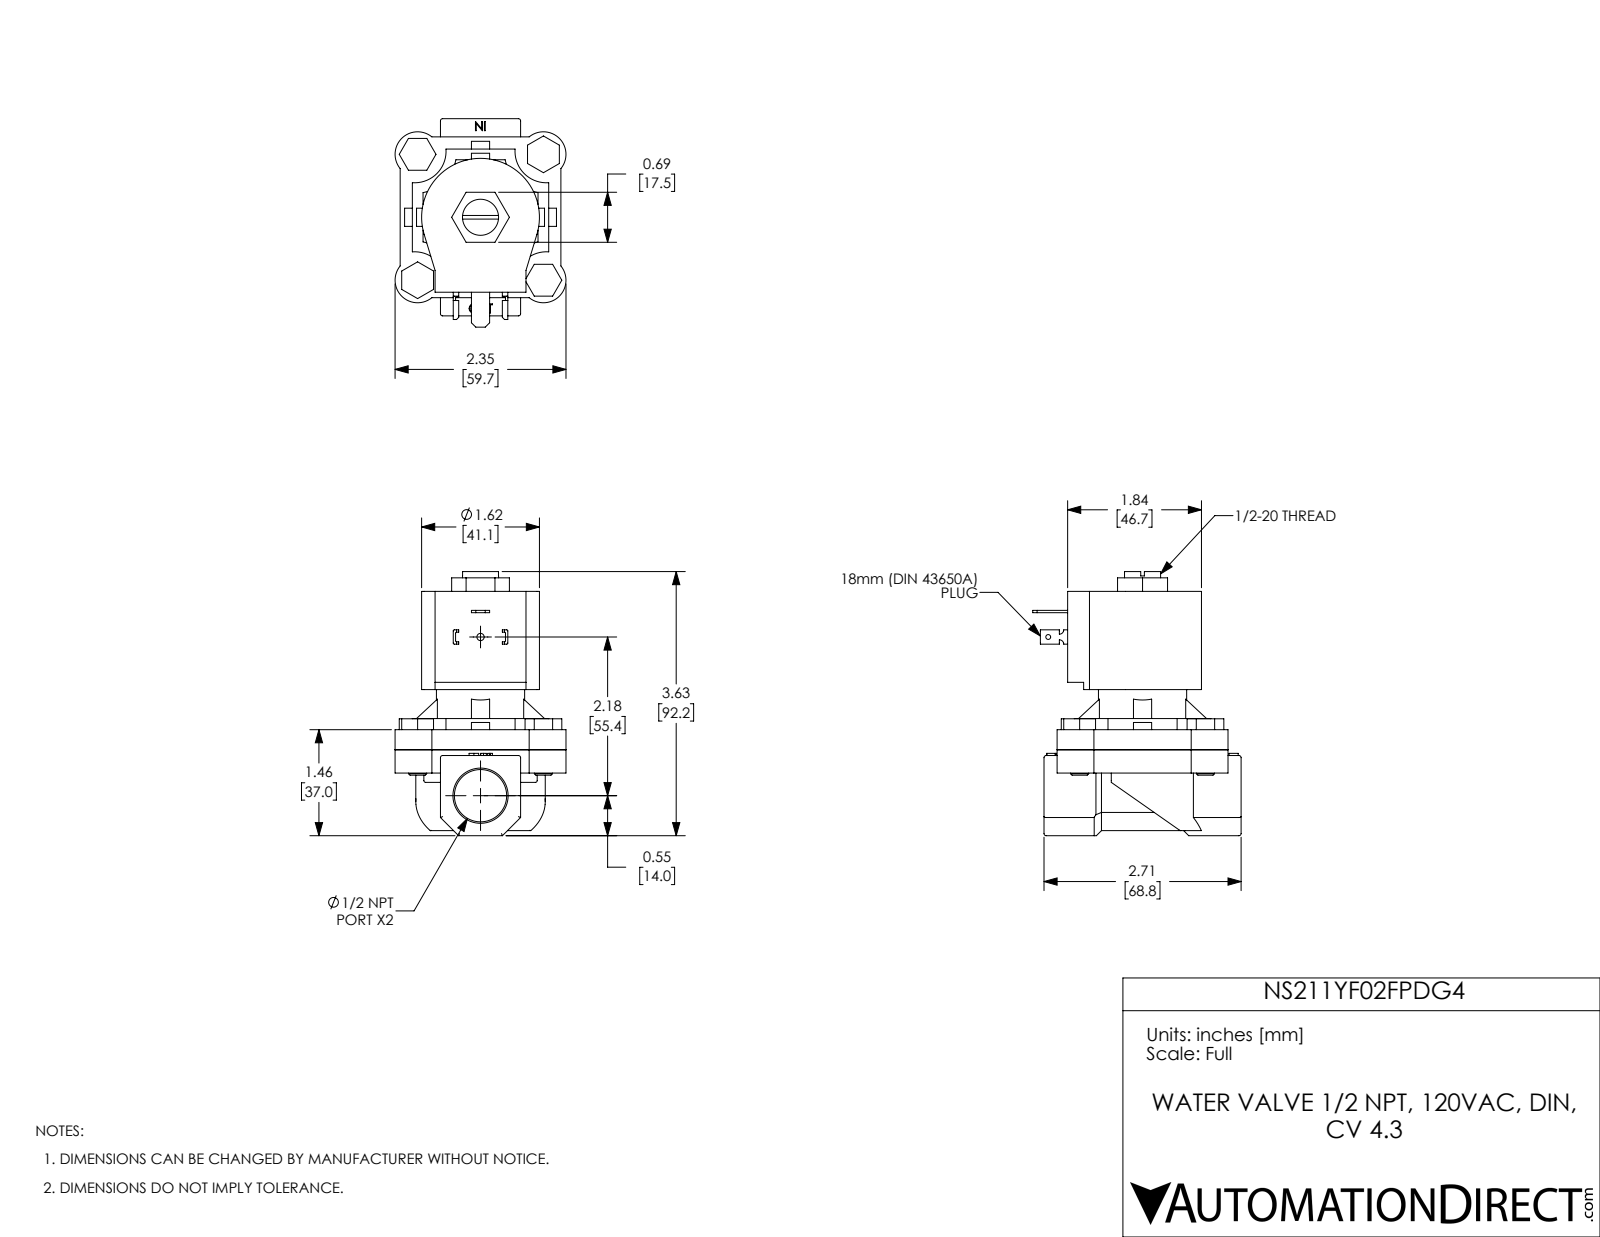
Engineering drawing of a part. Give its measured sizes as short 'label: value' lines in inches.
name: NS211YF02FPDG4
written by: SolidWorks 2017 (AUTOMOTIVE_DESIGN)
unit: in
bodies: 11 solids, 385 faces (239 planar, 113 cylindrical, 33 other)
size: 3.63 × 2.865 × 2.35
volume: 9.473 in³; area: 65.14 in²
holes: 4× ⌀0.25, 1× ⌀0.067, 1× ⌀0.1, 1× ⌀0.496, 1× ⌀0.512, 1× ⌀0.719, 1× ⌀1.155
bosses: 4× ⌀0.248, 1× ⌀1.213
rounds: 15× R0.03, 8× R0.015, 4× R0.31, 4× R0.432, 4× R0.579, 2× R0.06, 1× R0.81, 1× R0.89
face distances: 0.276, 2.177, 1.901, 0.32, 0.596, 2.497, 0.554, 1.656, 0.25, 1.147
hole spacings: 1.223, 1.73, 2.446, 2.181
